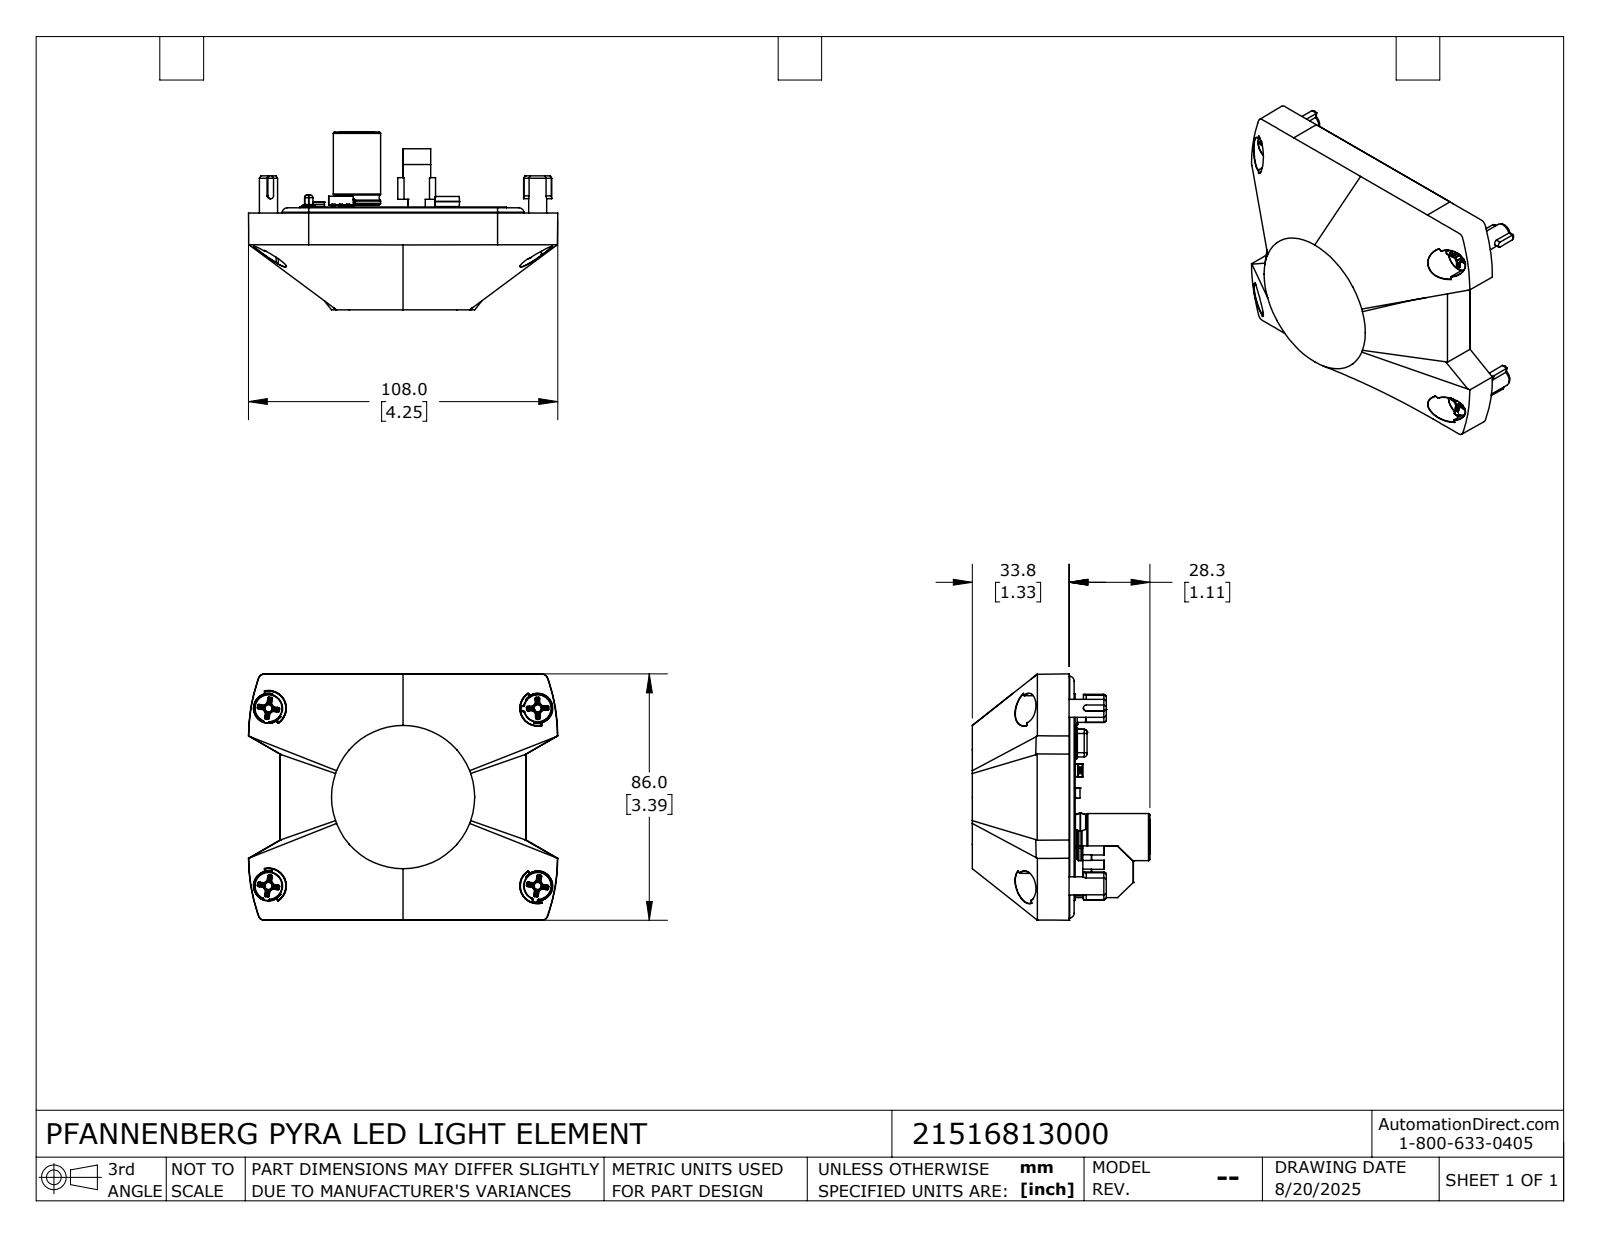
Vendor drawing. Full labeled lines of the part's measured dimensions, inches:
Part name (STEP PRODUCT): 21516813000
STEP written by: SolidWorks 2024 (CONFIG_CONTROL_DESIGN)
Units: inches
Bodies: 17 solids, 1949 faces (787 planar, 409 cylindrical, 753 other)
Overall size (bounding box): 4.252 × 3.386 × 2.444
Volume: 13.38 in³ · Surface area: 82.51 in²
Round holes (diameter × count): ⌀0.039 ×12, ⌀0.031 ×8, ⌀0.043 ×7, ⌀0.035 ×2, ⌀0.055 ×2, ⌀0.059 ×2, ⌀0.098 ×2, ⌀0.118 ×2, ⌀0.04 ×1, ⌀0.097 ×1, ⌀0.137 ×1, ⌀0.162 ×1
Round bosses / shafts (diameter × count): ⌀0.386 ×4, ⌀0.248 ×4, ⌀0.65 ×1
Partial cylindrical surfaces — rounded edges, fillets, slot ends (radius × count): R0.008 ×111, R0.004 ×8, R0.039 ×8, R0.063 ×8, R0.02 ×5, R0.057 ×4, R0.069 ×4, R0.072 ×4
Main face-to-face distances: 0.064, 0.138, 0.202, 1.414, 1.35, 1.213, 3.219, 3.189, 0.03, 0.02
Hole centre spacings: 0.2, 0.591, 1.494, 1.881, 0.188, 0.197, 0.394, 0.4
